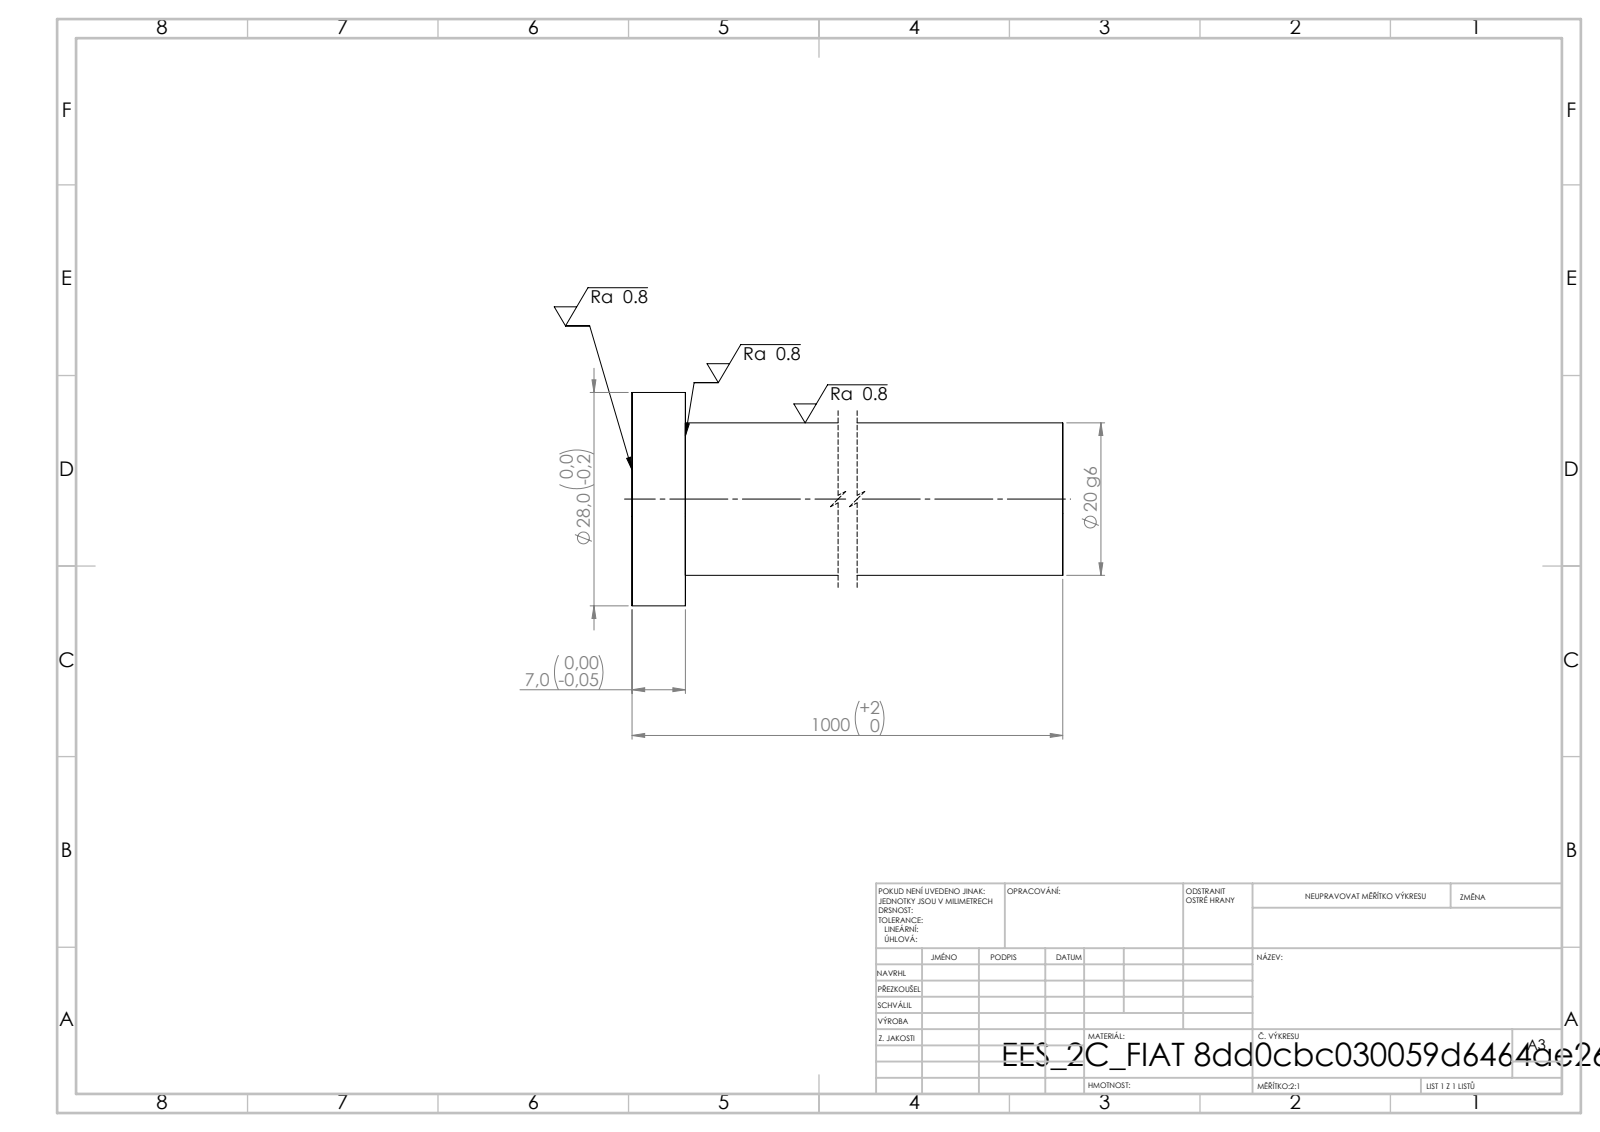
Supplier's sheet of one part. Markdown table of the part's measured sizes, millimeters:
| quantity | value |
| --- | --- |
| STEP written by | SolidWorks 2019 (CONFIG_CONTROL_DESIGN) |
| units | millimeters |
| bodies | 1 solid, 7 faces (3 planar, 4 cylindrical, 0 other) |
| overall size | 1000 × 28 × 28 |
| volume | 316 270 mm³ |
| surface area | 64 239 mm² |
| round bosses / shafts (diameter × count) | 28 × 1, 20 × 1 |
| main face-to-face distances | 1000, 7, 993 |
